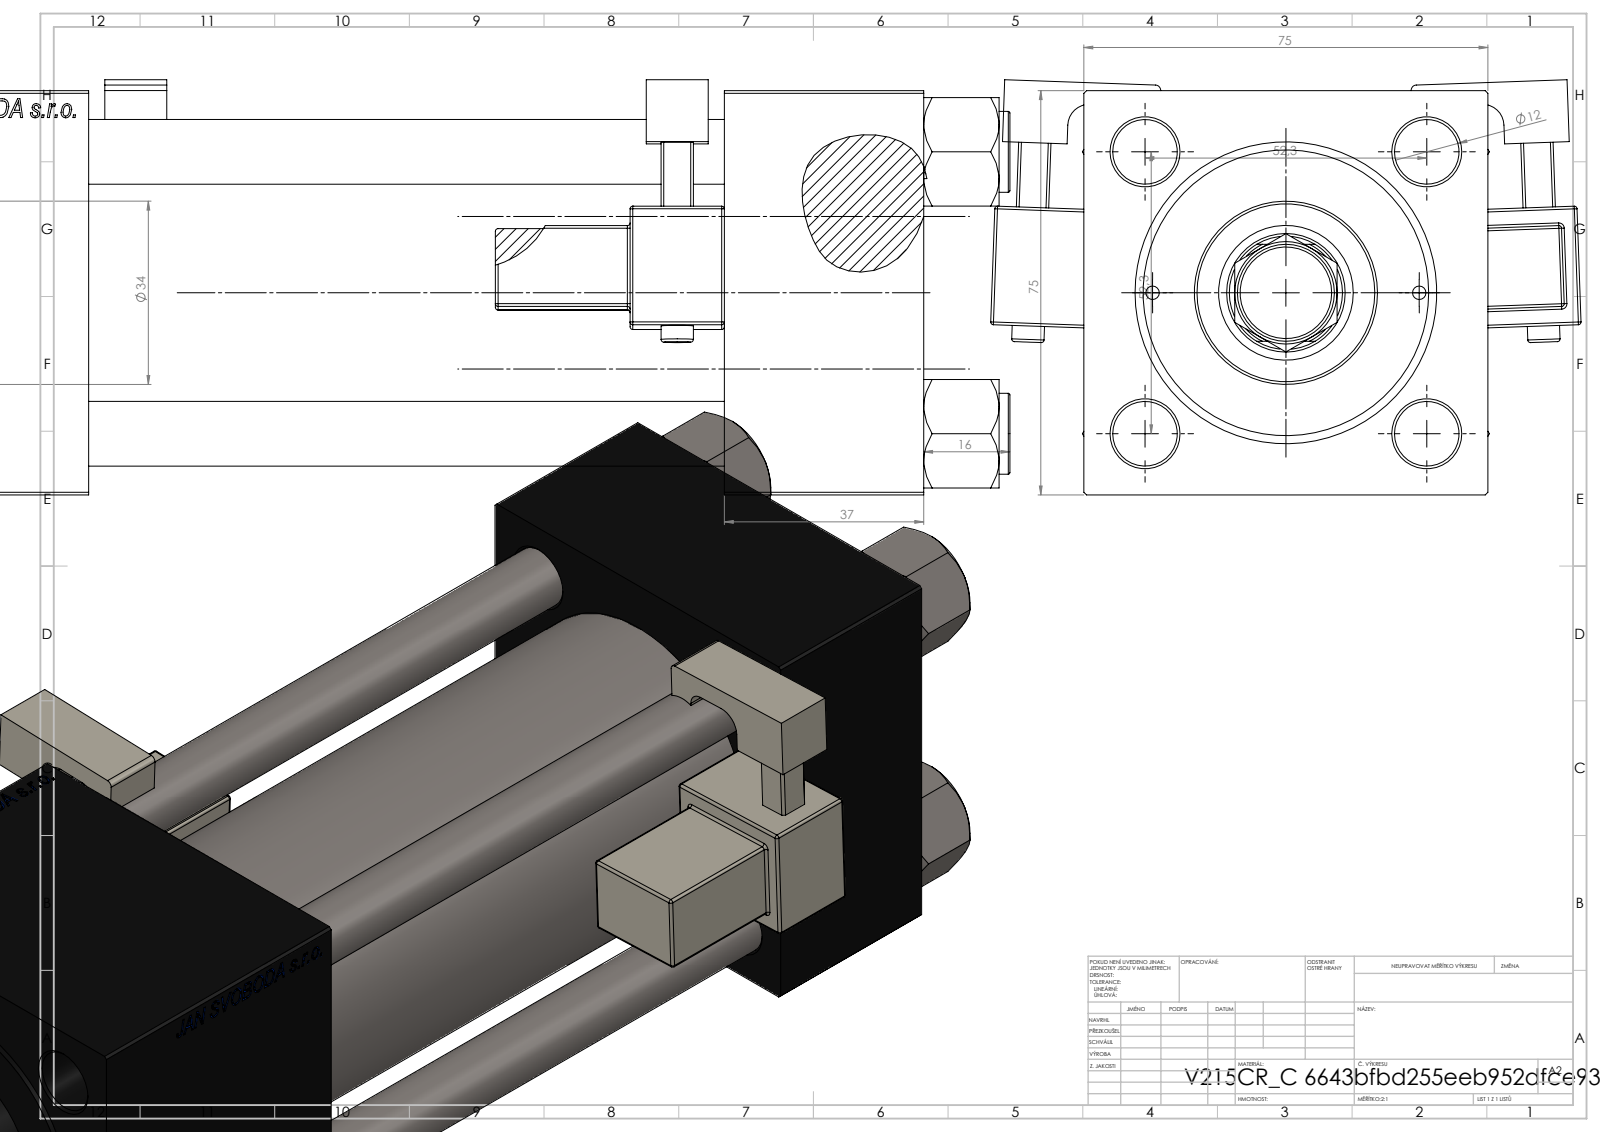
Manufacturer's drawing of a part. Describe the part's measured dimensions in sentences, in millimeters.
The part is named "V215CR_MSU; V215_VC_A; V215CR_C_Body; V215CR_VCP_C (+3 more)". Its 3-D file was written by "SolidWorks 2019 (CONFIG_CONTROL_DESIGN)". It is 14 solids with 1360 faces: 602 planar, 154 cylindrical and 604 other. Overall it measures 288 by 109.57 by 77.03 millimeters. Its volume is 786 052 cubic millimeters and its surface area 195 505 square millimeters. Round holes: 4 of diameter 12, 2 of diameter 2.5, 2 of diameter 7, 2 of diameter 20.96, 2 of diameter 30, 1 of diameter 10.5, 1 of diameter 22, 1 of diameter 25, 1 of diameter 41, 1 of diameter 50, 1 of diameter 53. Round bosses or shafts: 4 of diameter 15, 2 of diameter 6, 1 of diameter 56, 1 of diameter 34, 1 of diameter 18, 1 of diameter 11. Partial cylindrical surfaces (rounded edges, fillets, slot ends): 48 of radius 0.5, 2 of radius 1, 2 of radius 2.5, 2 of radius 4, 1 of radius 10.5. The main face-to-face distances are 75, 37, 214, 177, 155, 118, 59, 185.3, 148.3, 30.3. The hole center spacings are 26.19, 36.98, 52.3, 57.22, 24.75, 73.96, 49.5, 153.5.
